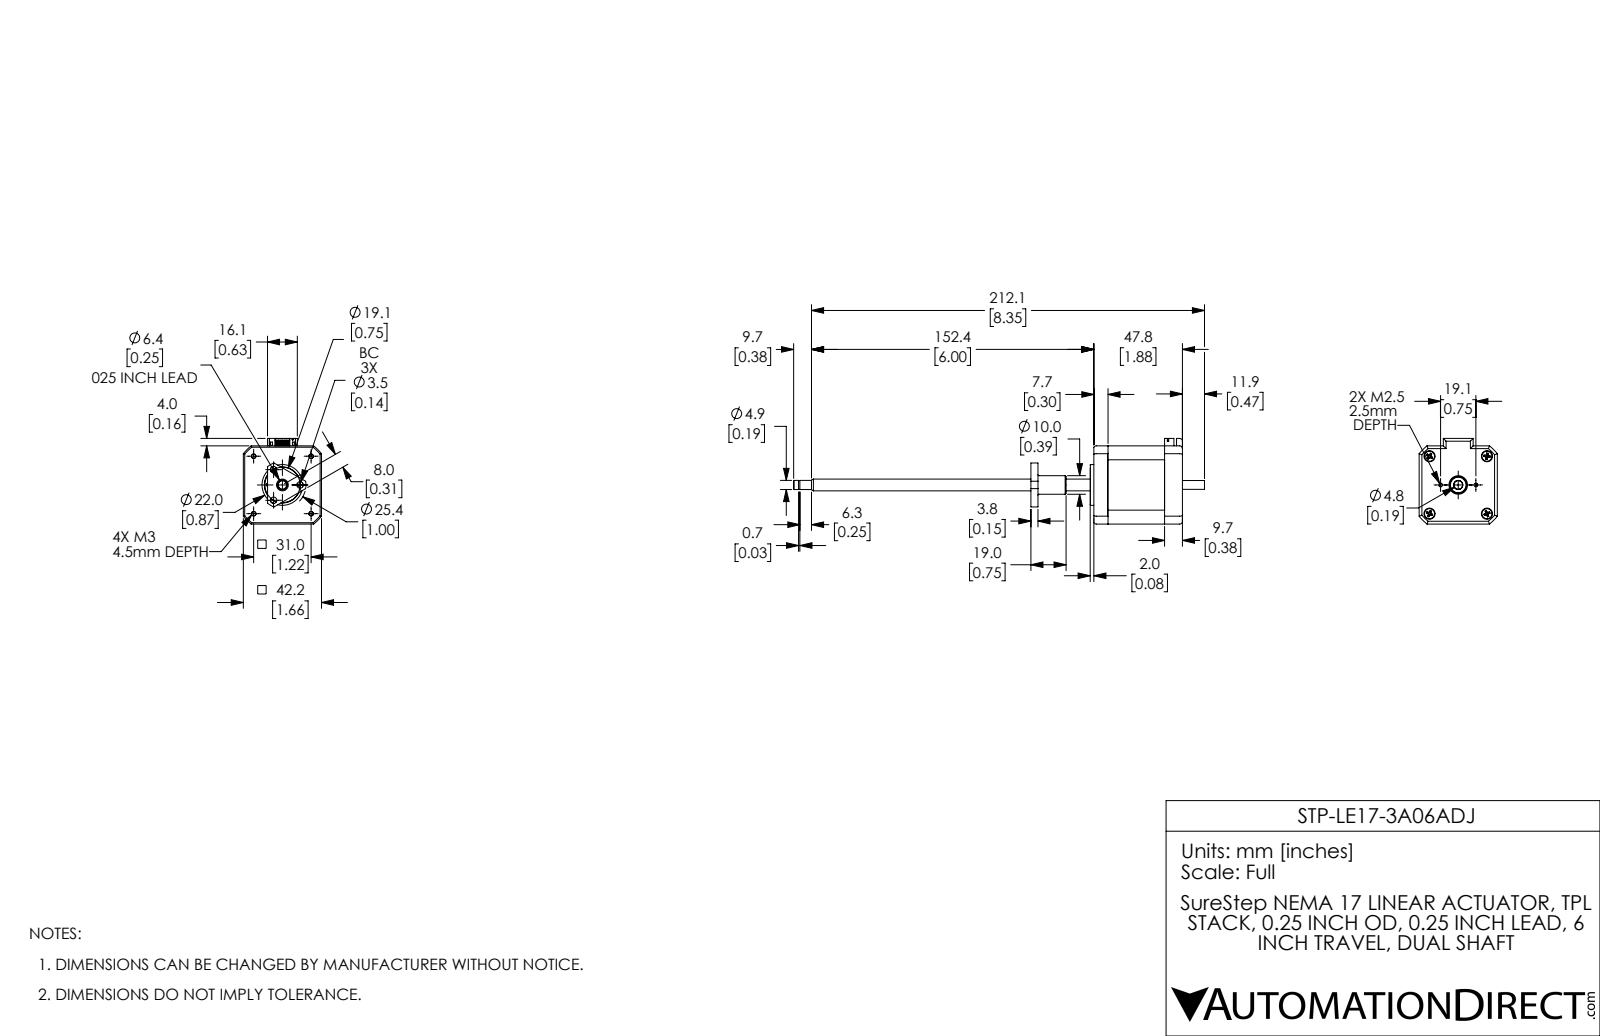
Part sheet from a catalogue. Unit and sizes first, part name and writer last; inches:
Units: inches
Overall size (bounding box): 8.73 × 1.819 × 1.661
Round holes (diameter × count): ⌀0.098 ×4, ⌀0.15 ×4, ⌀0.236 ×4, ⌀0.138 ×3, ⌀0.059 ×2, ⌀0.081 ×2, ⌀0.193 ×1, ⌀0.197 ×1, ⌀0.512 ×1, ⌀0.669 ×1, ⌀0.766 ×1, ⌀0.787 ×1
Round bosses / shafts (diameter × count): ⌀0.213 ×4, ⌀0.115 ×4, ⌀1.063 ×1, ⌀1.02 ×1, ⌀0.866 ×1, ⌀0.472 ×1, ⌀0.394 ×1, ⌀0.354 ×1
Partial cylindrical surfaces — rounded edges, fillets, slot ends (radius × count): R0.039 ×12, R0.059 ×11, R0.098 ×2, R0.028 ×1, R0.5 ×1, R0.561 ×1, R0.63 ×1, R0.988 ×1
Main face-to-face distances: 1.661, 0.38, 1.502, 1.882, 1.581, 0.063, 1.201, 0.301, 0.039, 1.783
Hole centre spacings: 0.654, 0.375, 0.863, 1.159, 1.22, 0.194, 0.315, 0.51
Volume: 4.804 in³ · Surface area: 46.33 in²
Bodies: 6 solids, 749 faces (368 planar, 246 cylindrical, 135 other)
Part name (STEP PRODUCT): STP-LE17-3A06ADJ; STP-LE17-3A06ADJ_2; STP-LE17-3A06ADJ_1
STEP written by: SolidWorks 2017 (AUTOMOTIVE_DESIGN)
